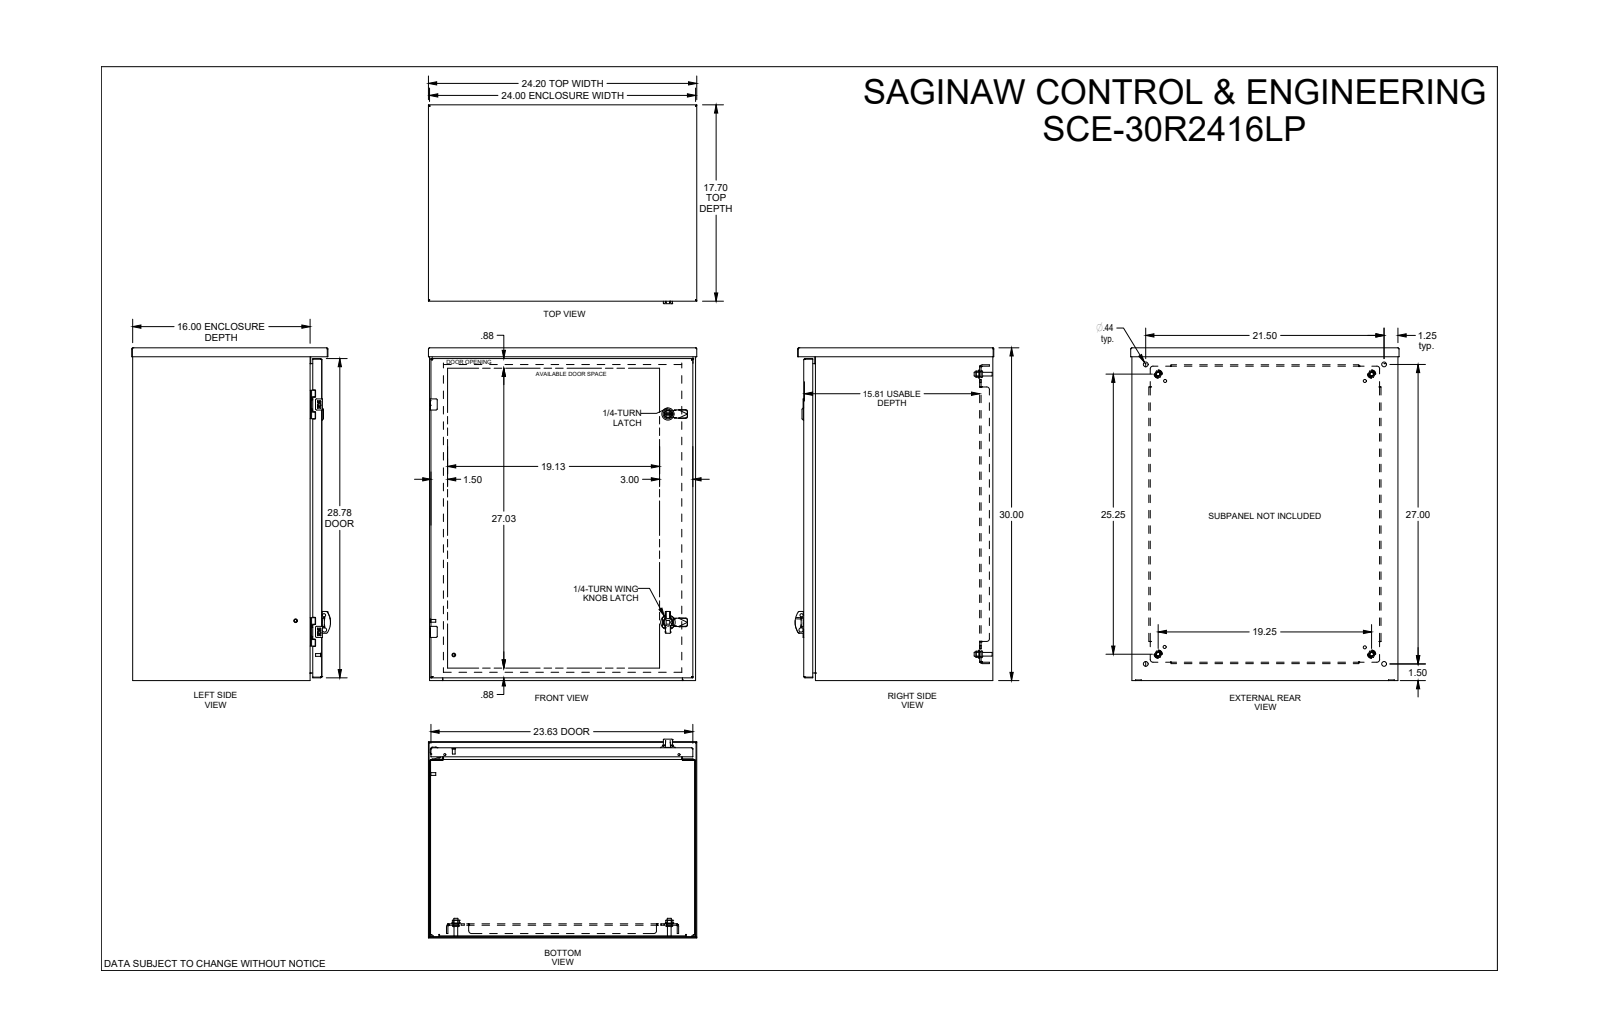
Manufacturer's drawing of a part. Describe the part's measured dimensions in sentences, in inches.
The part is named "SCE-30R2416LP". Its 3-D file was written by "SolidWorks 2019 (CONFIG_CONTROL_DESIGN)". It is 0 solids with 2429 faces: 1160 planar, 823 cylindrical and 446 other. Overall it measures 30 by 24.2 by 17.927 inches. Round holes: 4 of diameter 0.172, 4 of diameter 0.205, 4 of diameter 0.244, 4 of diameter 0.266, 4 of diameter 0.281, 4 of diameter 0.367, 4 of diameter 0.375, 4 of diameter 0.438, 4 of diameter 0.5, 2 of diameter 0.04, 2 of diameter 0.156, 2 of diameter 0.188. Round bosses or shafts: 6 of diameter 0.17, 4 of diameter 0.366, 4 of diameter 0.332, 4 of diameter 0.25, 4 of diameter 0.24, 3 of diameter 0.196, 2 of diameter 0.866, 2 of diameter 0.802. Partial cylindrical surfaces (rounded edges, fillets, slot ends): 72 of radius 0.015, 60 of radius 0.012, 26 of radius 0.01, 24 of radius 0.02, 23 of radius 0.112, 22 of radius 0.06, 19 of radius 0.052, 15 of radius 0.03. The main face-to-face distances are 0.06, 23.94, 29.94, 0.06, 16.933, 16.993, 17.053, 16.993, 0.125, 1. The hole center spacings are 20.5, 0.024, 0.493, 0.875, 0.985, 20.394, 2.296, 18.641.
